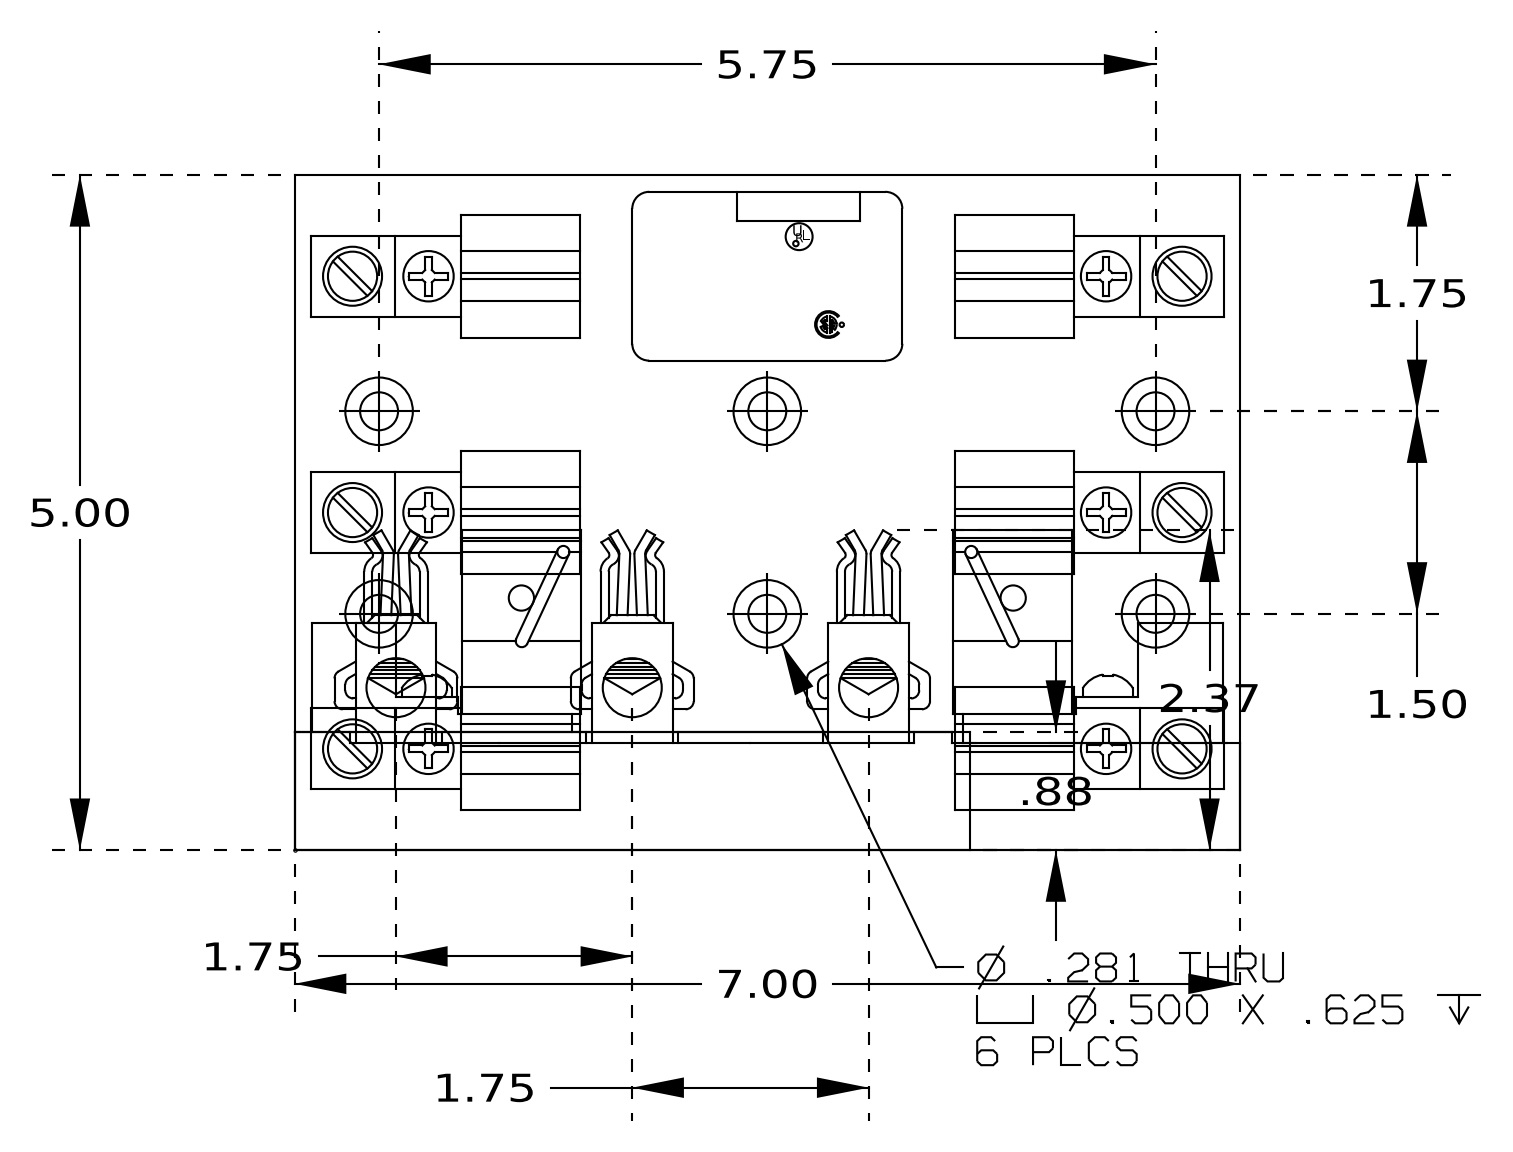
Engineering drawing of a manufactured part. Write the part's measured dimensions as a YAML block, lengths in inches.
part_name: "700507rev"
step_written_by: "SolidWorks 2016 (AUTOMOTIVE_DESIGN)"
units: inches
bodies: {solids: 25, faces: 1565, planar: 656, cylindrical: 260, other: 649}
overall_size: [7, 5, 1.55]
volume: 13.84
surface_area: 236.6
round_holes:
  - {diameter: 0.159, count: 12}
  - {diameter: 0.1, count: 6}
  - {diameter: 0.236, count: 6}
  - {diameter: 0.324, count: 6}
  - {diameter: 0.332, count: 6}
  - {diameter: 0.4, count: 6}
  - {diameter: 0.437, count: 3}
round_bosses_or_shafts:
  - {diameter: 0.25, count: 6}
  - {diameter: 0.19, count: 6}
  - {diameter: 0.375, count: 5}
  - {diameter: 0.375, count: 1}
partial_cylinders:
  - {radius: 0.04, count: 8}
face_to_face_distances: [1.75, 0.08, 0.112, 0.125, 0.045, 0.125, 3.5, 0.755, 1.13, 0.88]
hole_center_spacings: [1.75, 1.838, 3.5, 2.229, 2.615, 4.039, 4.552, 5.85]
